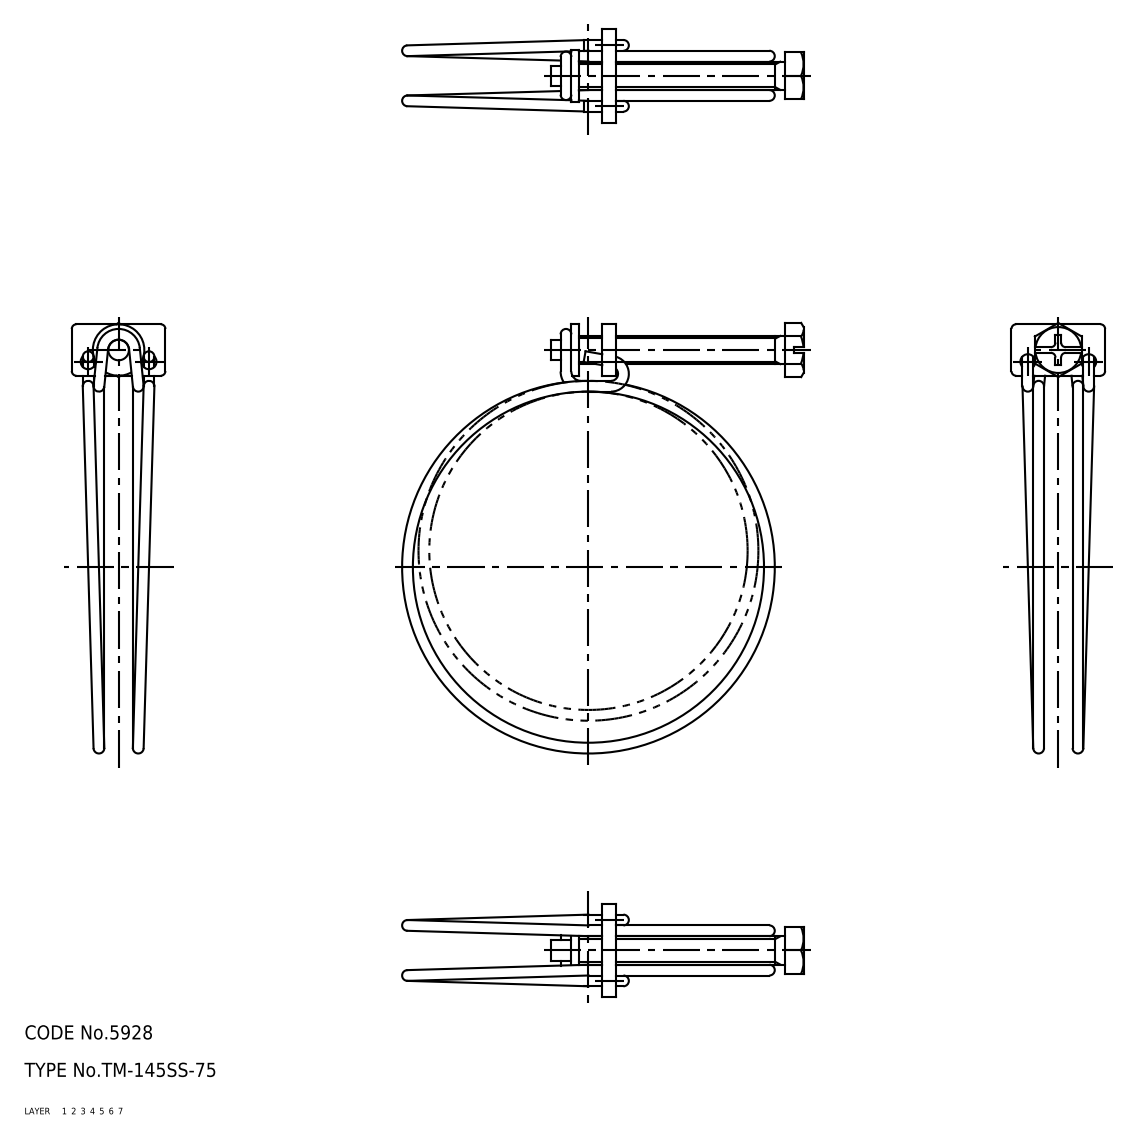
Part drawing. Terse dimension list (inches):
name: holder; band; TM_145SS_75; screw
written by: SolidWorks 2015 (AUTOMOTIVE_DESIGN)
unit: in
bodies: 3 solids, 95 faces (31 planar, 36 cylindrical, 28 other)
size: 3.628 × 3.377 × 0.787
volume: 0.282 in³; area: 9.495 in²
holes: 2× ⌀0.126, 1× ⌀0.236
bosses: 8× ⌀0.091, 1× ⌀0.433, 1× ⌀0.173
rounds: 8× R0.039
face distances: 0.118, 0.197, 0.26, 0.378, 0.433, 0.063, 0.315, 0.394, 1.953, 1.89
hole spacings: 0.274, 0.512
